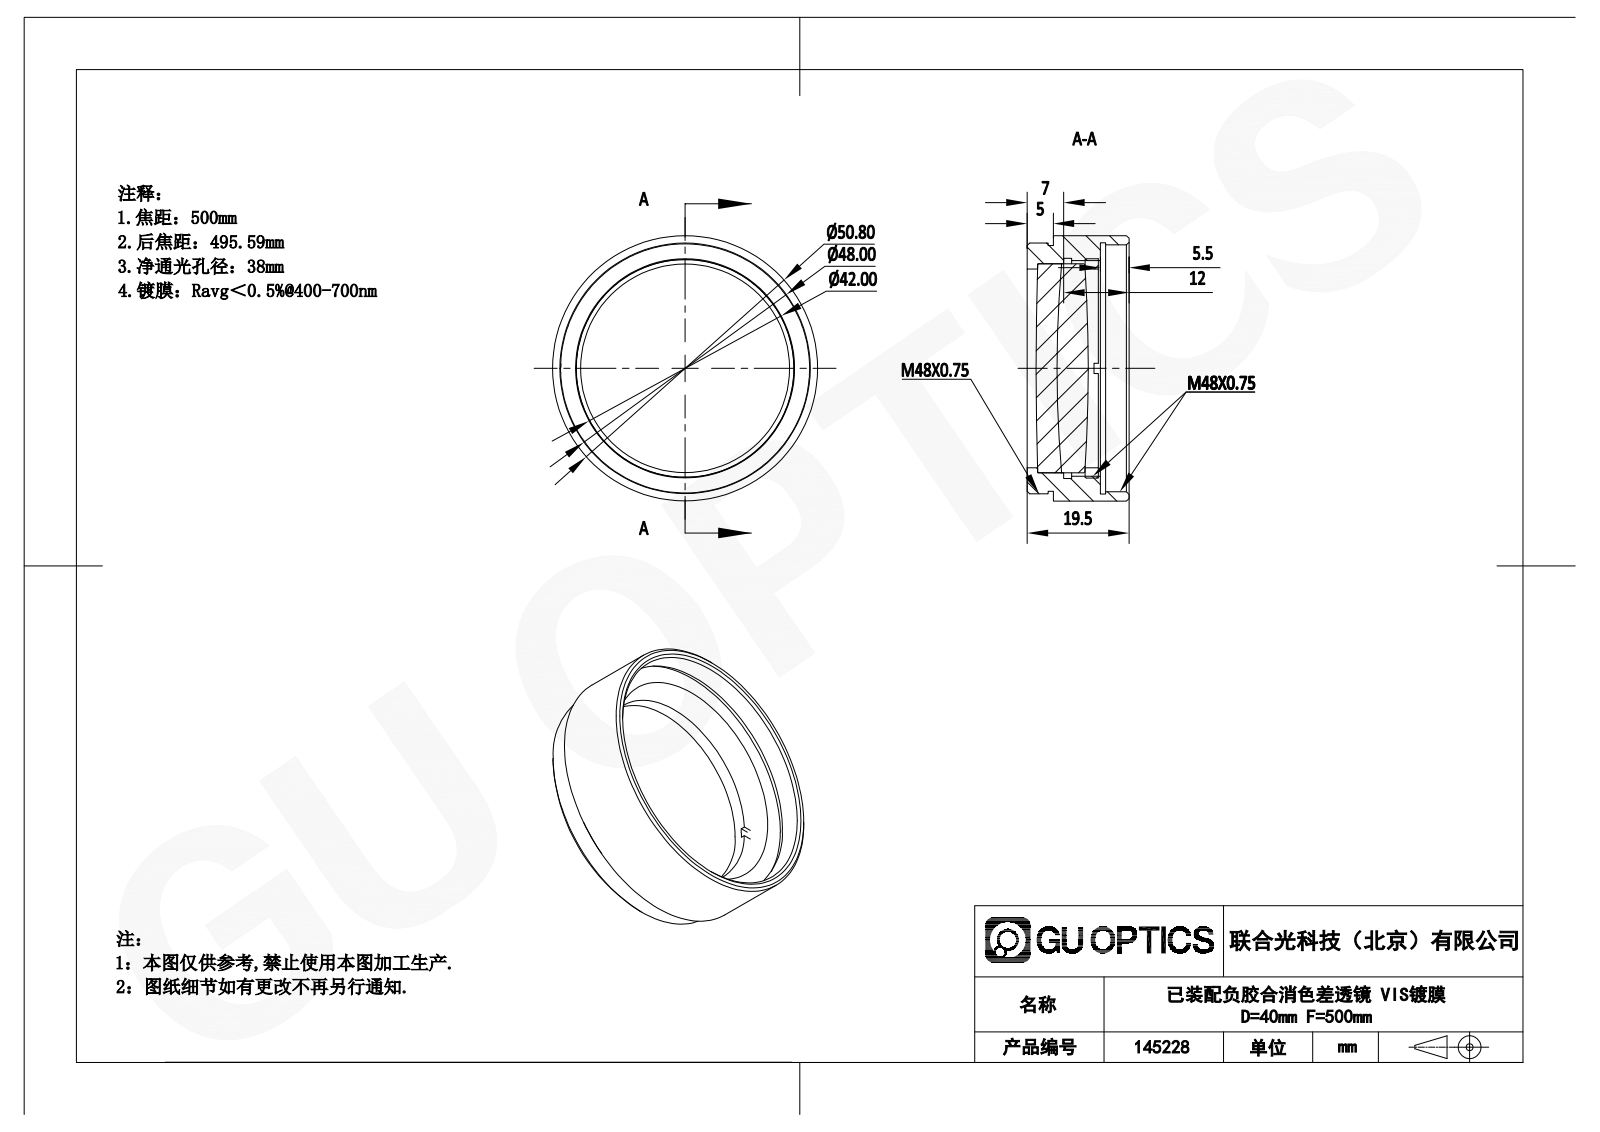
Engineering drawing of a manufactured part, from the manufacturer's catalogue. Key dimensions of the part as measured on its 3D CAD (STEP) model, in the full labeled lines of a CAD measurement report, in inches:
Part name (STEP PRODUCT): GL31-040-500-VIS_Solidworks; APD-ML40-500-VIS-A; M42x0.75ѹȦ
STEP written by: SolidWorks 2022 (AUTOMOTIVE_DESIGN)
Units: inches
Bodies: 4 solids, 64 faces (18 planar, 26 cylindrical, 20 other)
Overall size (bounding box): 2 × 2 × 0.768
Volume: 1.415 in³ · Surface area: 23.19 in²
Round holes (diameter × count): ⌀1.496 ×1, ⌀1.624 ×1, ⌀1.657 ×1, ⌀1.86 ×1, ⌀1.894 ×1
Round bosses / shafts (diameter × count): ⌀2 ×1, ⌀1.89 ×1, ⌀1.85 ×1, ⌀1.654 ×1, ⌀1.575 ×1
Main face-to-face distances: 0.551, 0.197, 0.079, 0.354, 0.276, 0.536, 0.339, 0.015, 0.437, 0.241
